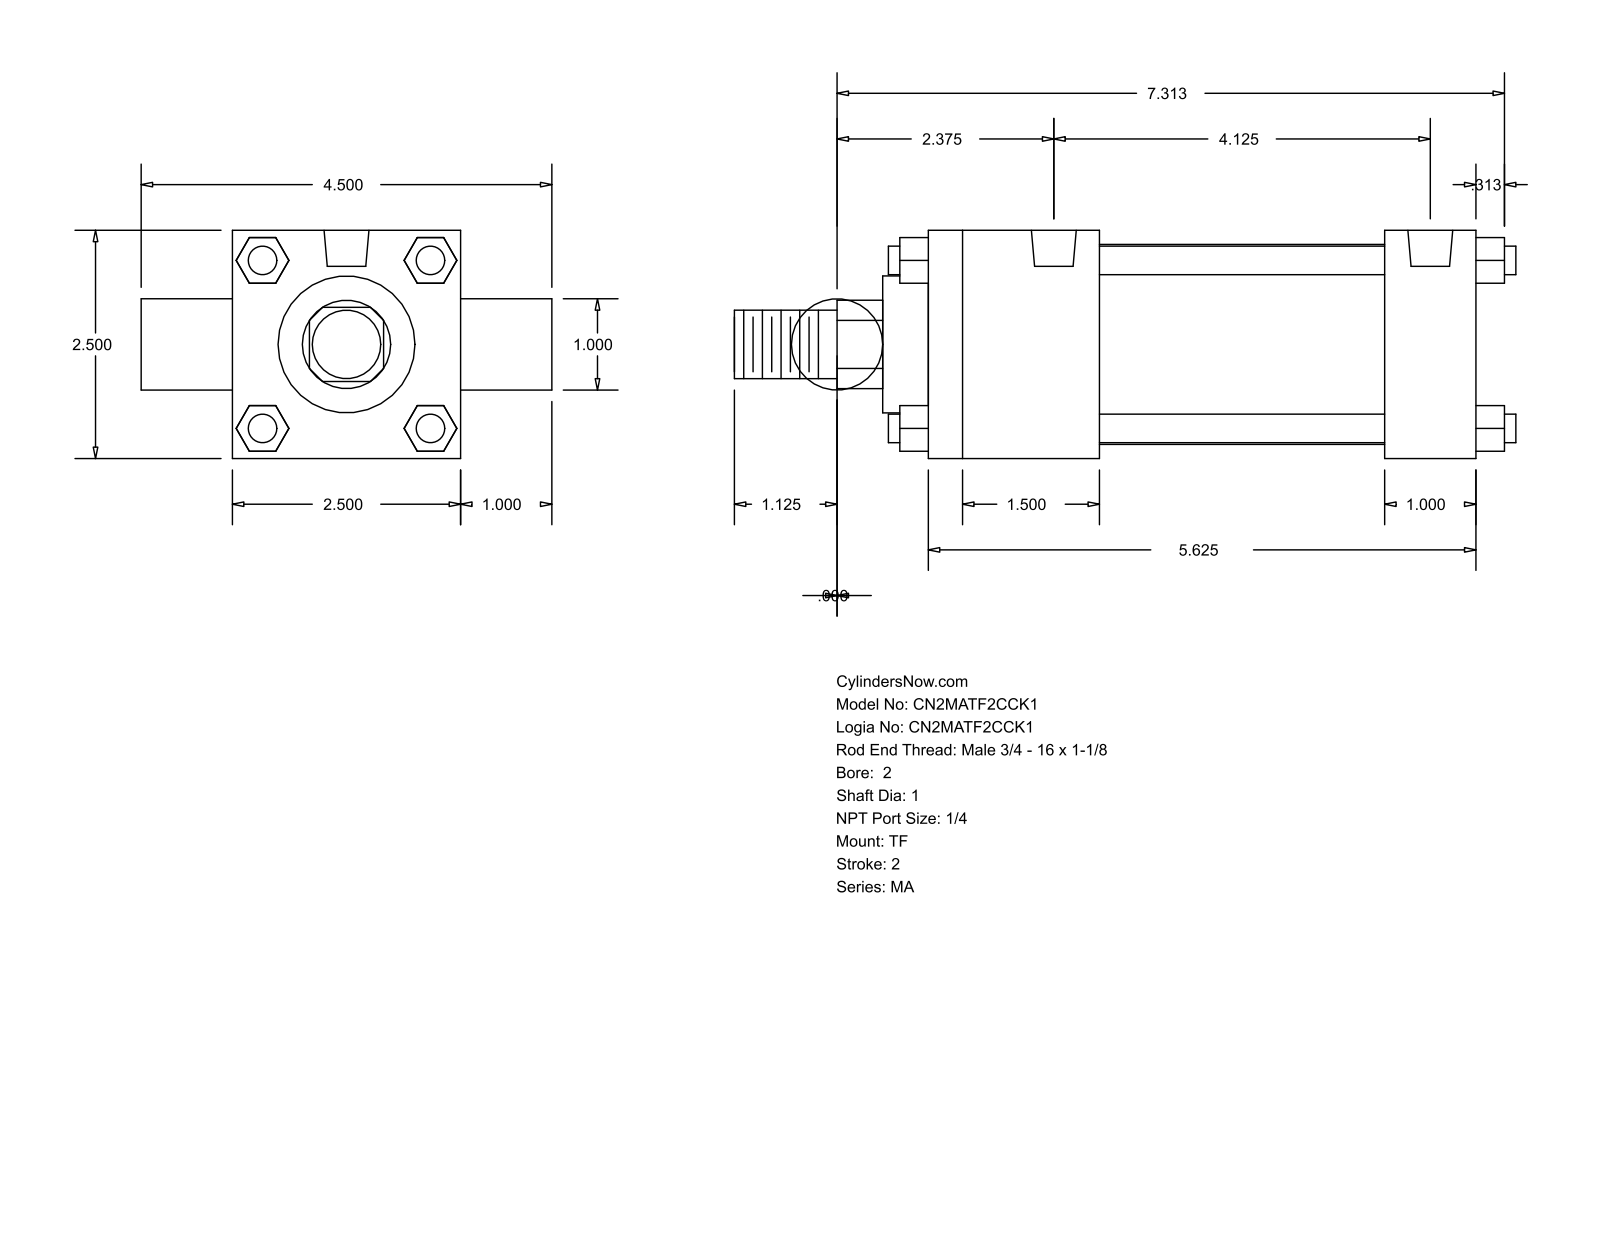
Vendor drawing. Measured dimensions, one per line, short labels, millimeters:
name: MA_TF__0200_1
written by: GSSL Pune (CONFIG_CONTROL_DESIGN)
unit: mm
bodies: 0 solids, 120 faces (92 planar, 28 cylindrical, 0 other)
size: 217.49 × 114.3 × 63.5
holes: 3× ⌀7.94, 2× ⌀12.49
bosses: 4× ⌀7.94, 2× ⌀25.4, 1× ⌀55.63, 1× ⌀38.1, 1× ⌀19.05
rounds: 1× R12.29
face distances: 63.5, 25.4, 152.4, 12.7, 47.63, 127, 79.37, 104.77, 88.9, 40.47
hole spacings: 104.77
